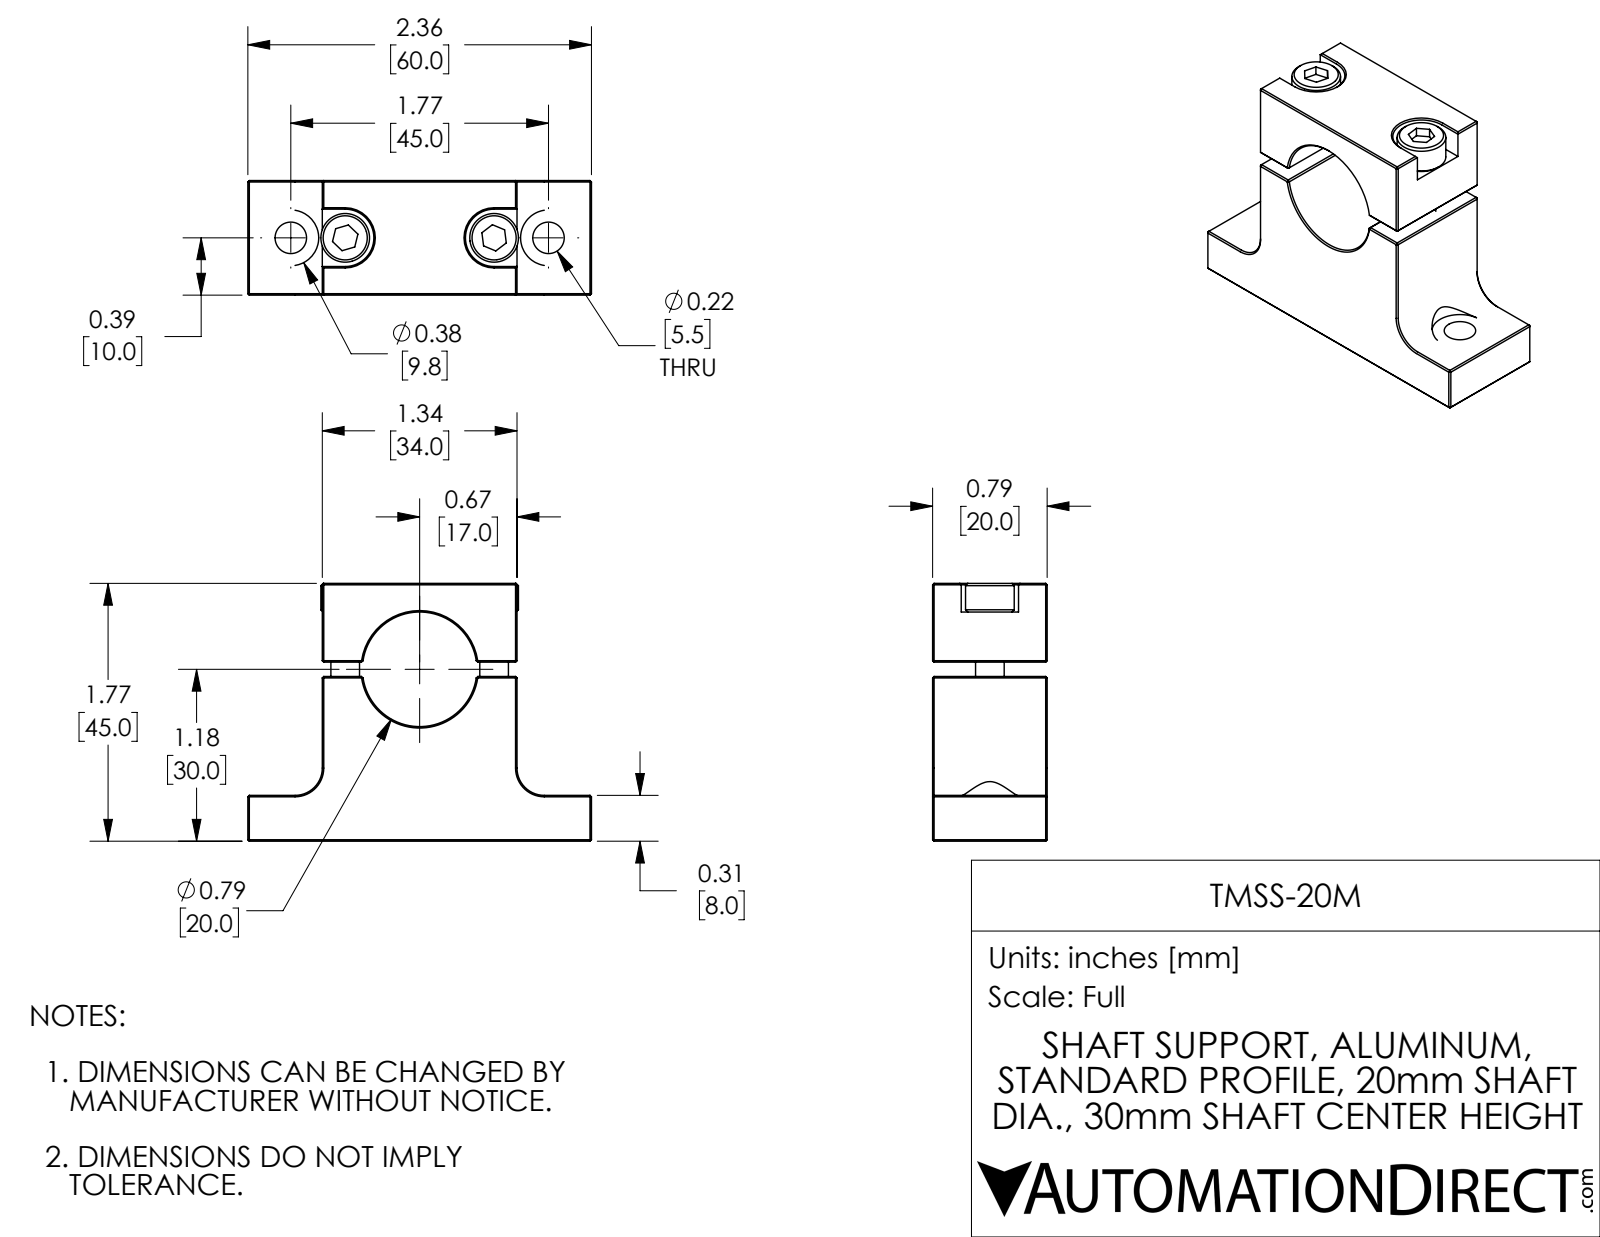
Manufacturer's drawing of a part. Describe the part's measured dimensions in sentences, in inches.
The part is named "TMSS-20M". Its 3-D file was written by "SolidWorks 2017 (AUTOMOTIVE_DESIGN)". It is 4 solids with 176 faces: 120 planar, 32 cylindrical and 24 other. Overall it measures 2.362 by 1.772 by 0.787 inches. Its volume is 1.628 cubic inches and its surface area 16.54 square inches. Round holes: 4 of diameter 0.217, 2 of diameter 0.163, 1 of diameter 0.094, 1 of diameter 0.787. Round bosses or shafts: 2 of diameter 0.335, 2 of diameter 0.197. Partial cylindrical surfaces (rounded edges, fillets, slot ends): 2 of radius 0.187, 2 of radius 0.192, 2 of radius 0.197. The main face-to-face distances are 0.787, 1.772, 1.339, 0.315, 1.457, 0.512, 1.85, 0.197, 1.132, 0.817. The hole center spacings are 0.374, 0.512, 0.886, 1.398, 1.024, 1.772.
